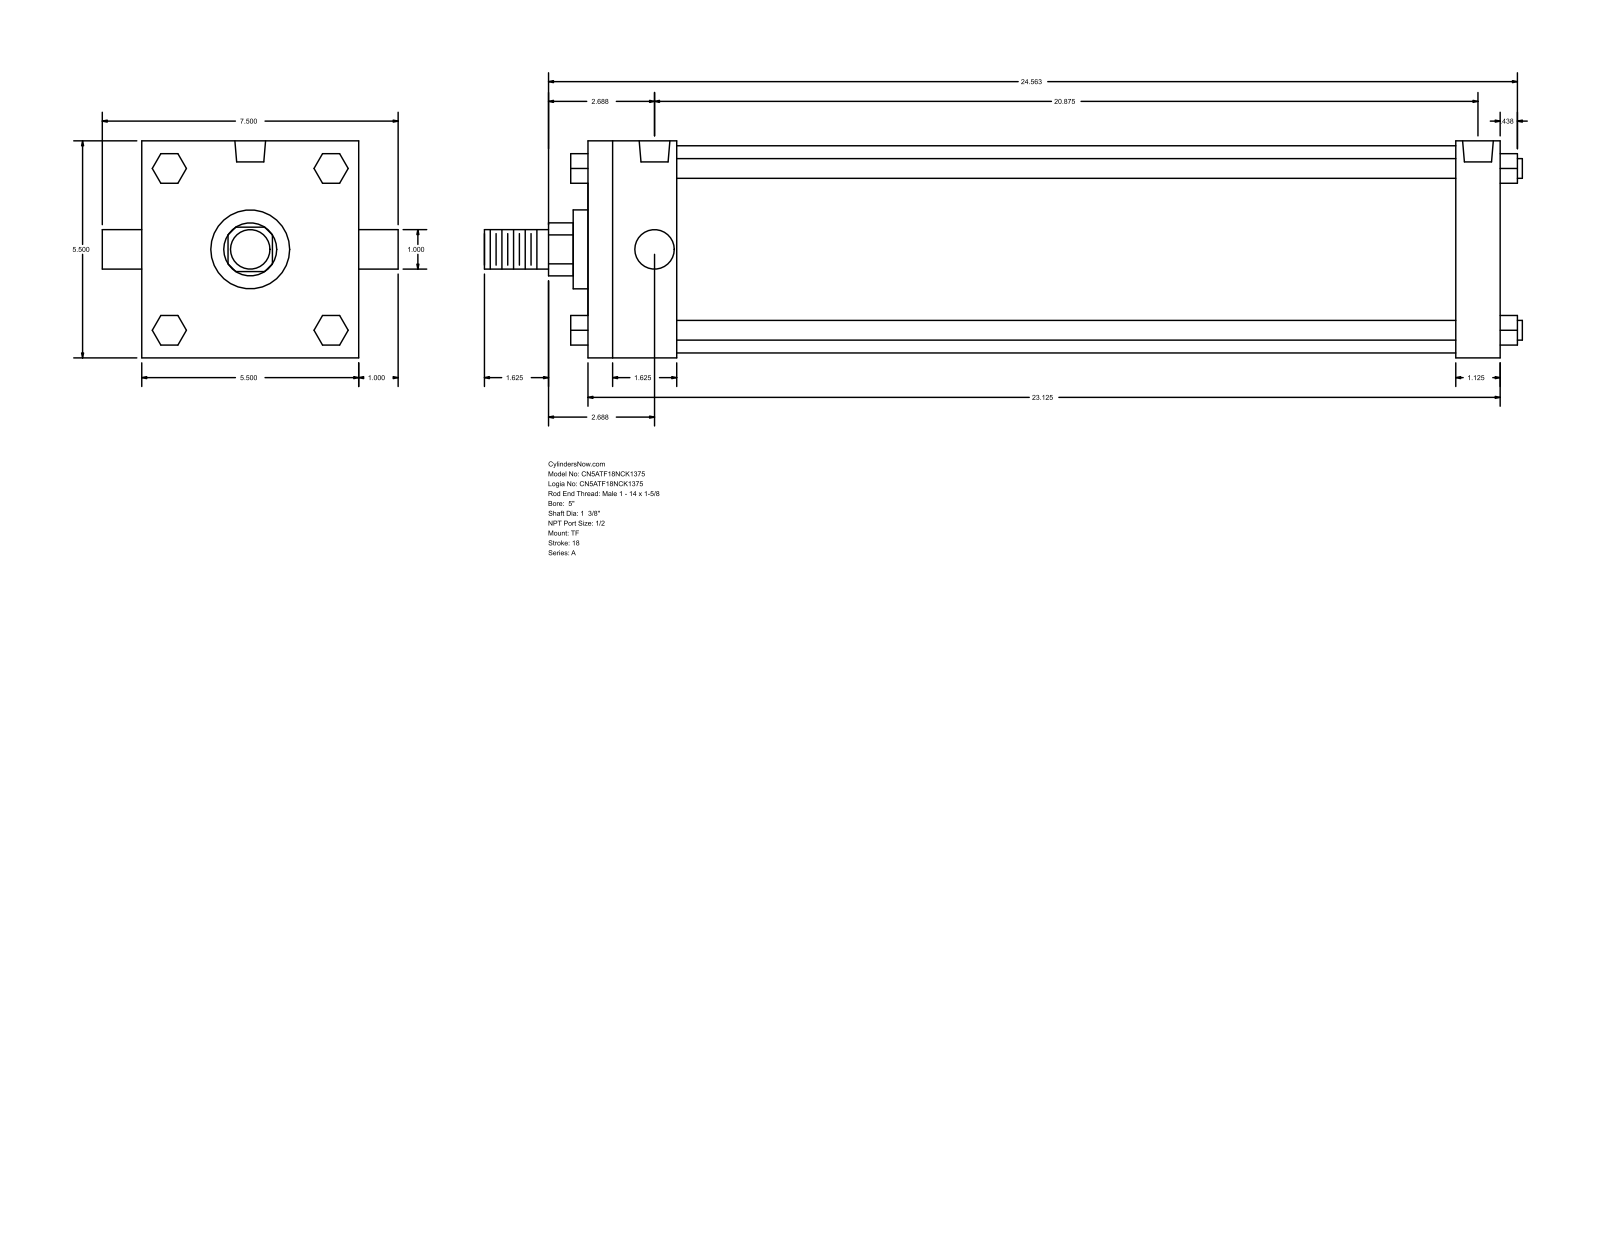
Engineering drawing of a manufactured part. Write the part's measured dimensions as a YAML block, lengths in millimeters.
part_name: "A_TF__0500_1.375"
step_written_by: "GSSL Pune (CONFIG_CONTROL_DESIGN)"
units: millimeters
bodies: {solids: 0, faces: 120, planar: 92, cylindrical: 28, other: 0}
overall_size: [668.34, 190.5, 139.7]
round_holes:
  - {diameter: 8.73, count: 3}
  - {diameter: 19.77, count: 2}
round_bosses_or_shafts:
  - {diameter: 12.7, count: 4}
  - {diameter: 25.4, count: 2}
  - {diameter: 133.35, count: 1}
  - {diameter: 50.8, count: 1}
  - {diameter: 34.92, count: 1}
partial_cylinders:
  - {radius: 17.06, count: 1}
face_to_face_distances: [139.7, 587.37, 57.15, 558.8, 28.57, 501.65, 530.22, 19.05, 52.07, 90.18]
hole_center_spacings: [2.39, 527.84, 525.45, 530.23]
